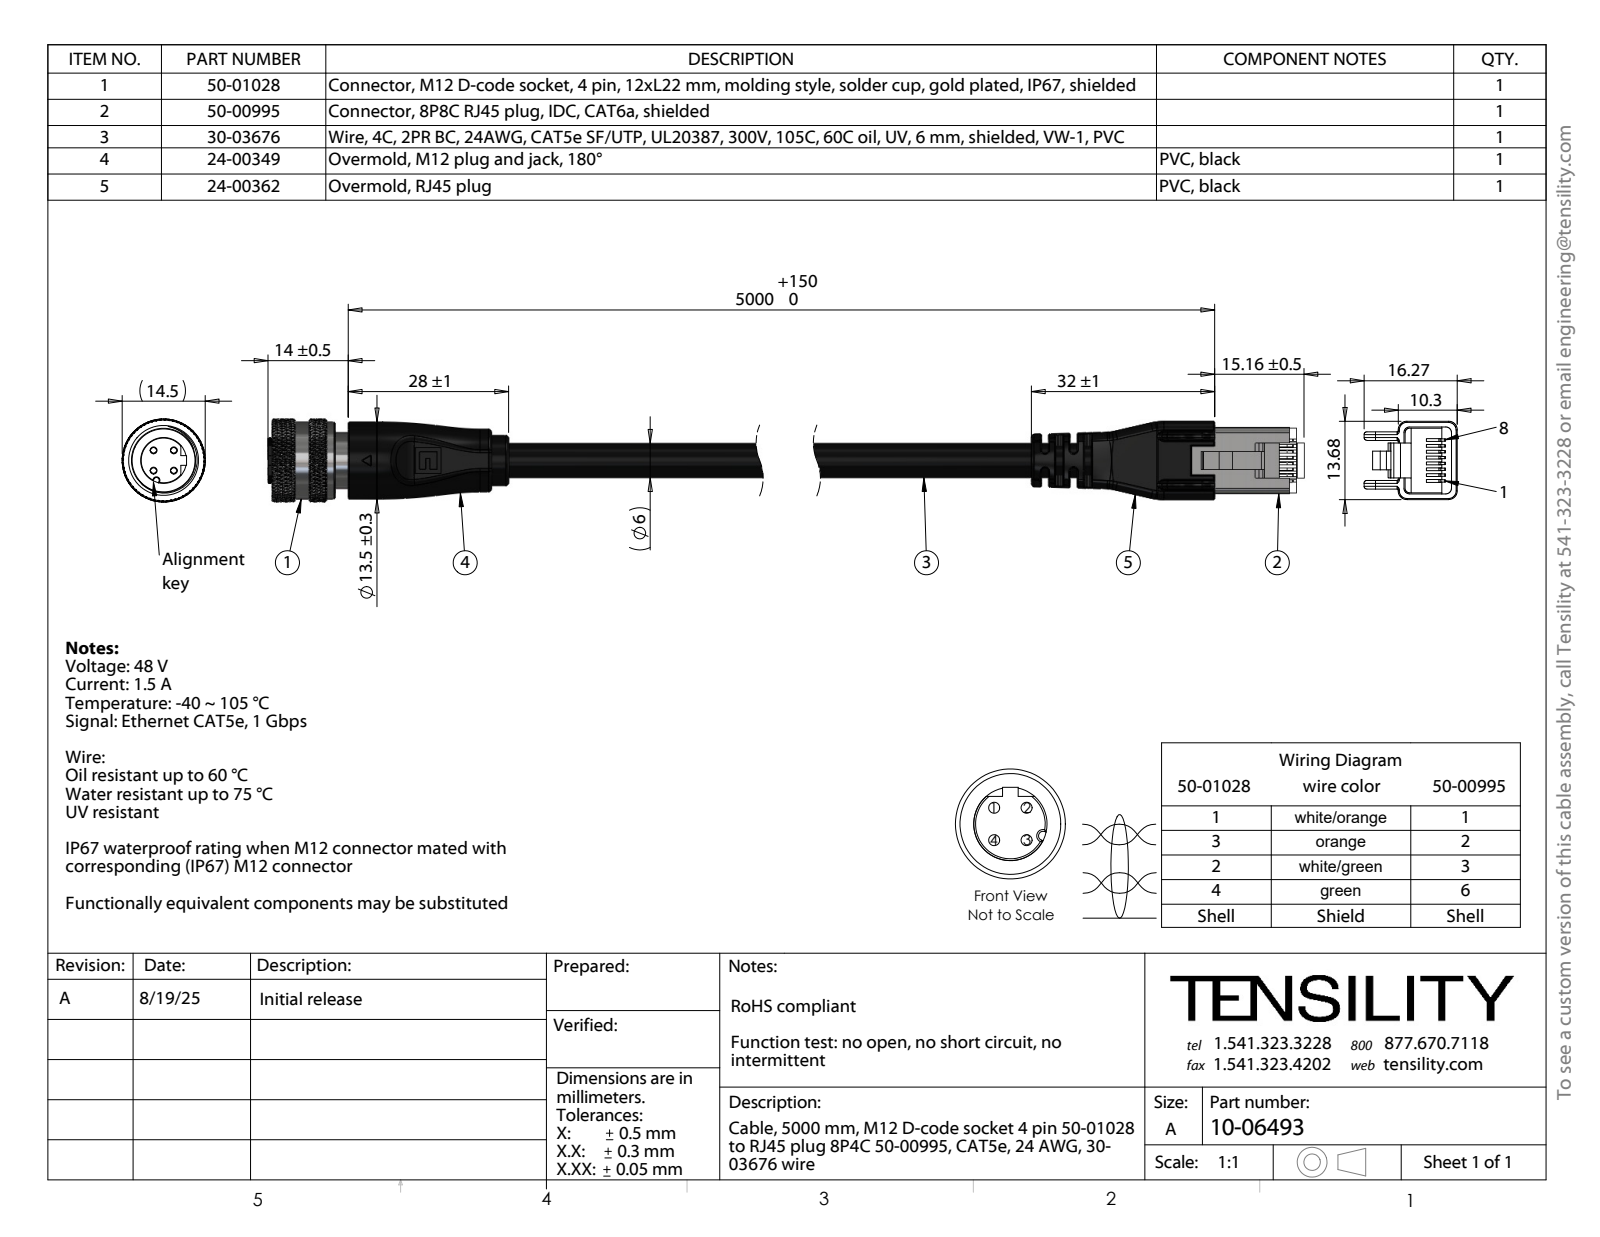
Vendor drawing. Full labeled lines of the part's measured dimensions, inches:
Part name (STEP PRODUCT): 50-01028-03_默认; 50-00995; 50-01028-02_默认; 50-01028-01_默认 (+7 more)
STEP written by: SolidWorks 2025 (CONFIG_CONTROL_DESIGN)
Units: inches
Bodies: 55 solids, 3967 faces (546 planar, 928 cylindrical, 2493 other)
Overall size (bounding box): 9.02 × 0.723 × 0.571
Volume: 0.869 in³ · Surface area: 46.04 in²
Round holes (diameter × count): ⌀0.008 ×28, ⌀0.041 ×4, ⌀0.043 ×4, ⌀0.047 ×4, ⌀0.124 ×1, ⌀0.126 ×1, ⌀0.14 ×1, ⌀0.354 ×1, ⌀0.394 ×1, ⌀0.441 ×1
Round bosses / shafts (diameter × count): ⌀0.063 ×4, ⌀0.059 ×4, ⌀0.531 ×1, ⌀0.433 ×1, ⌀0.417 ×1, ⌀0.413 ×1, ⌀0.386 ×1, ⌀0.382 ×1
Partial cylindrical surfaces — rounded edges, fillets, slot ends (radius × count): R0.008 ×11, R0.004 ×10, R0.02 ×10, R0.059 ×10, R0.024 ×8, R0.016 ×6, R0.039 ×5, R0.394 ×4
Main face-to-face distances: 0.049, 0.039, 0.098, 0.148, 0.366, 0.197, 0.059, 7.854, 0.499, 0.335
Hole centre spacings: 0.075, 0.014, 0.082, 0.042, 0.035, 0.043, 0.049, 0.071
